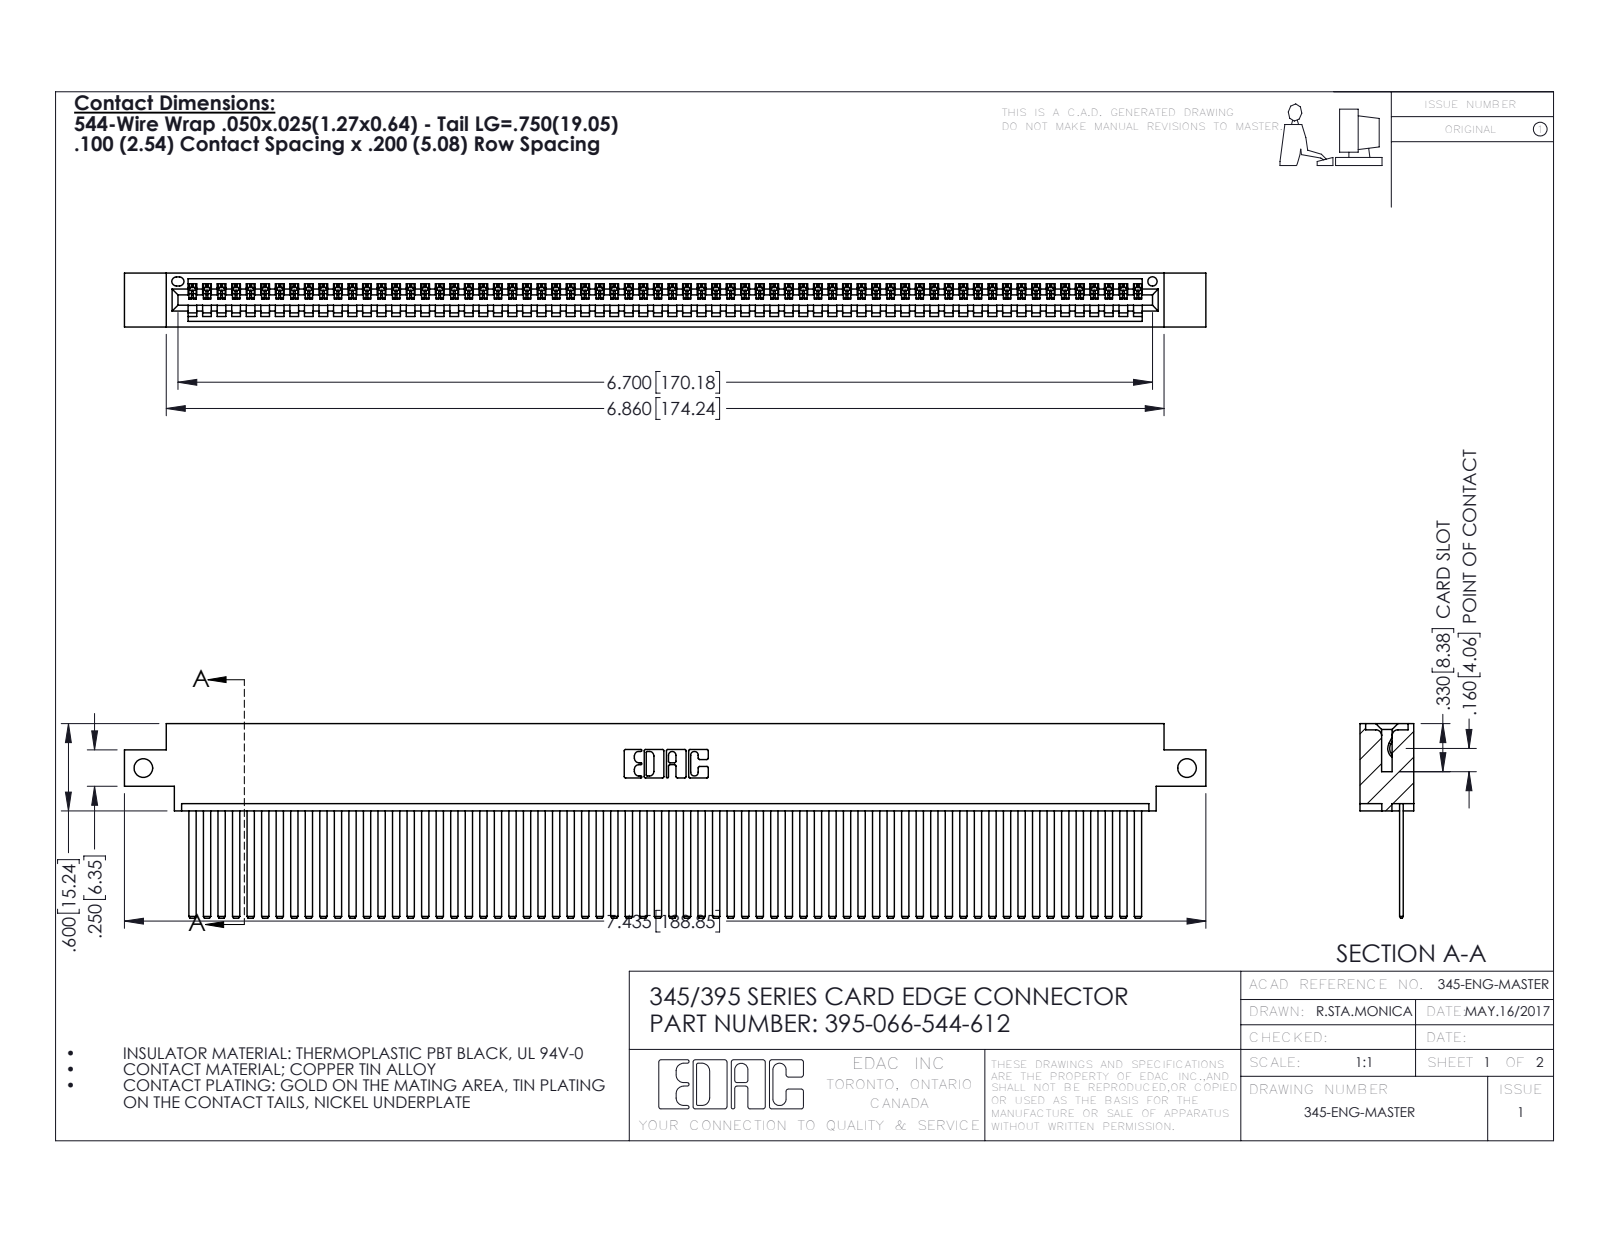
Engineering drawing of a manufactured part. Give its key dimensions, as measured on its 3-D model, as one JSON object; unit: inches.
{"part_name": "345 Part_0.170 Offset - Side Mount; 345-292-001_345-293-144; 395-066-544-612", "step_written_by": "SolidWorks 2016 (CONFIG_CONTROL_DESIGN)", "units": "inches", "bodies": {"solids": 67, "faces": 3562, "planar": 2460, "cylindrical": 1102, "other": 0}, "overall_size": [7.435, 1.337, 0.37], "volume_in3": 1.141, "surface_area_in2": 42.55, "round_holes": [[0.128, 2], [0.064, 1]], "partial_cylinders_radius": [[0.006, 132], [0.01, 22], [0.007, 6], [0.031, 6], [0.026, 3], [0.031, 2], [0.04, 2], [0.014, 1]], "face_to_face_distances": [0.072, 0.298, 0.025, 0.098, 0.272, 0.37, 0.2, 0.225, 0.175, 0.149], "hole_center_spacings": [7.175]}
